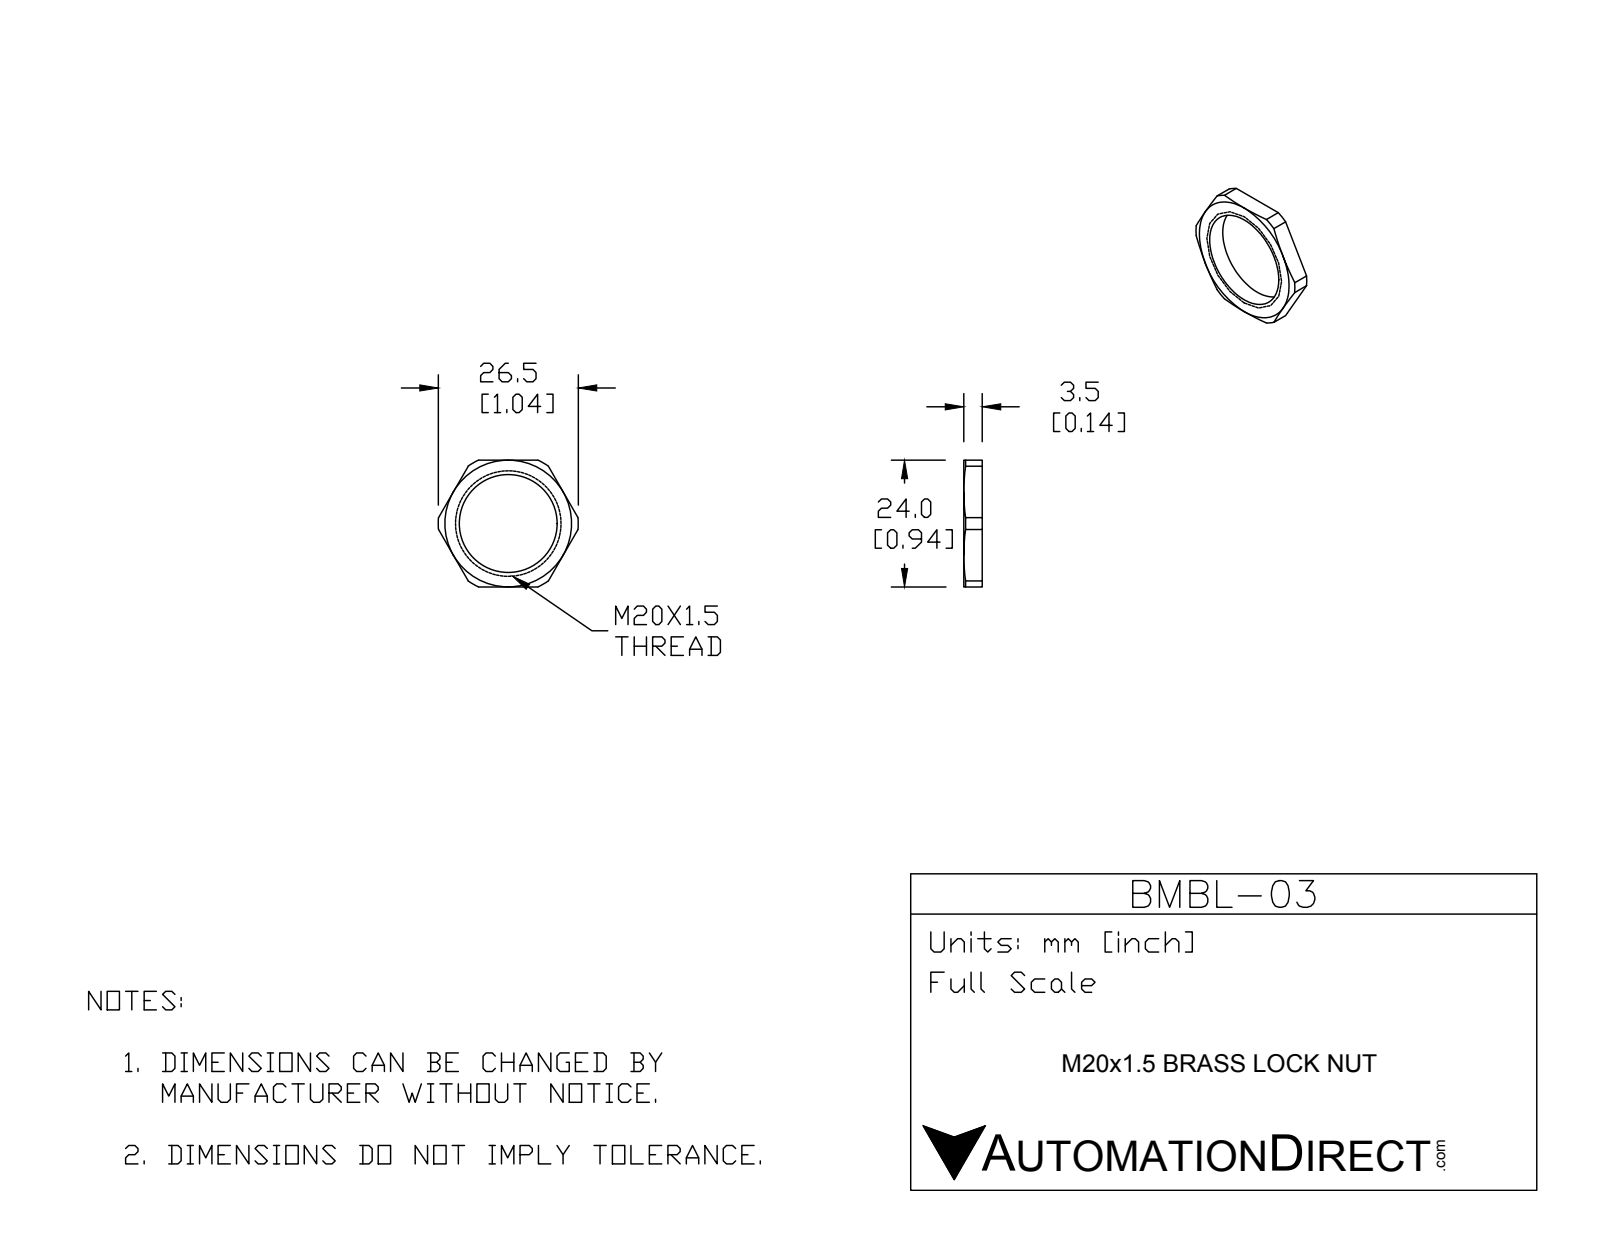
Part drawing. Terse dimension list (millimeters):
name: BMBL-03
written by: SolidWorks 2015 (CONFIG_CONTROL_DESIGN)
unit: mm
bodies: 1 solid, 23 faces (8 planar, 9 cylindrical, 6 other)
size: 26.5 × 24 × 3.5
volume: 786 mm³; area: 928 mm²
holes: 1× ⌀18.5
rounds: 1× R13.25
face distances: 3.5, 24
